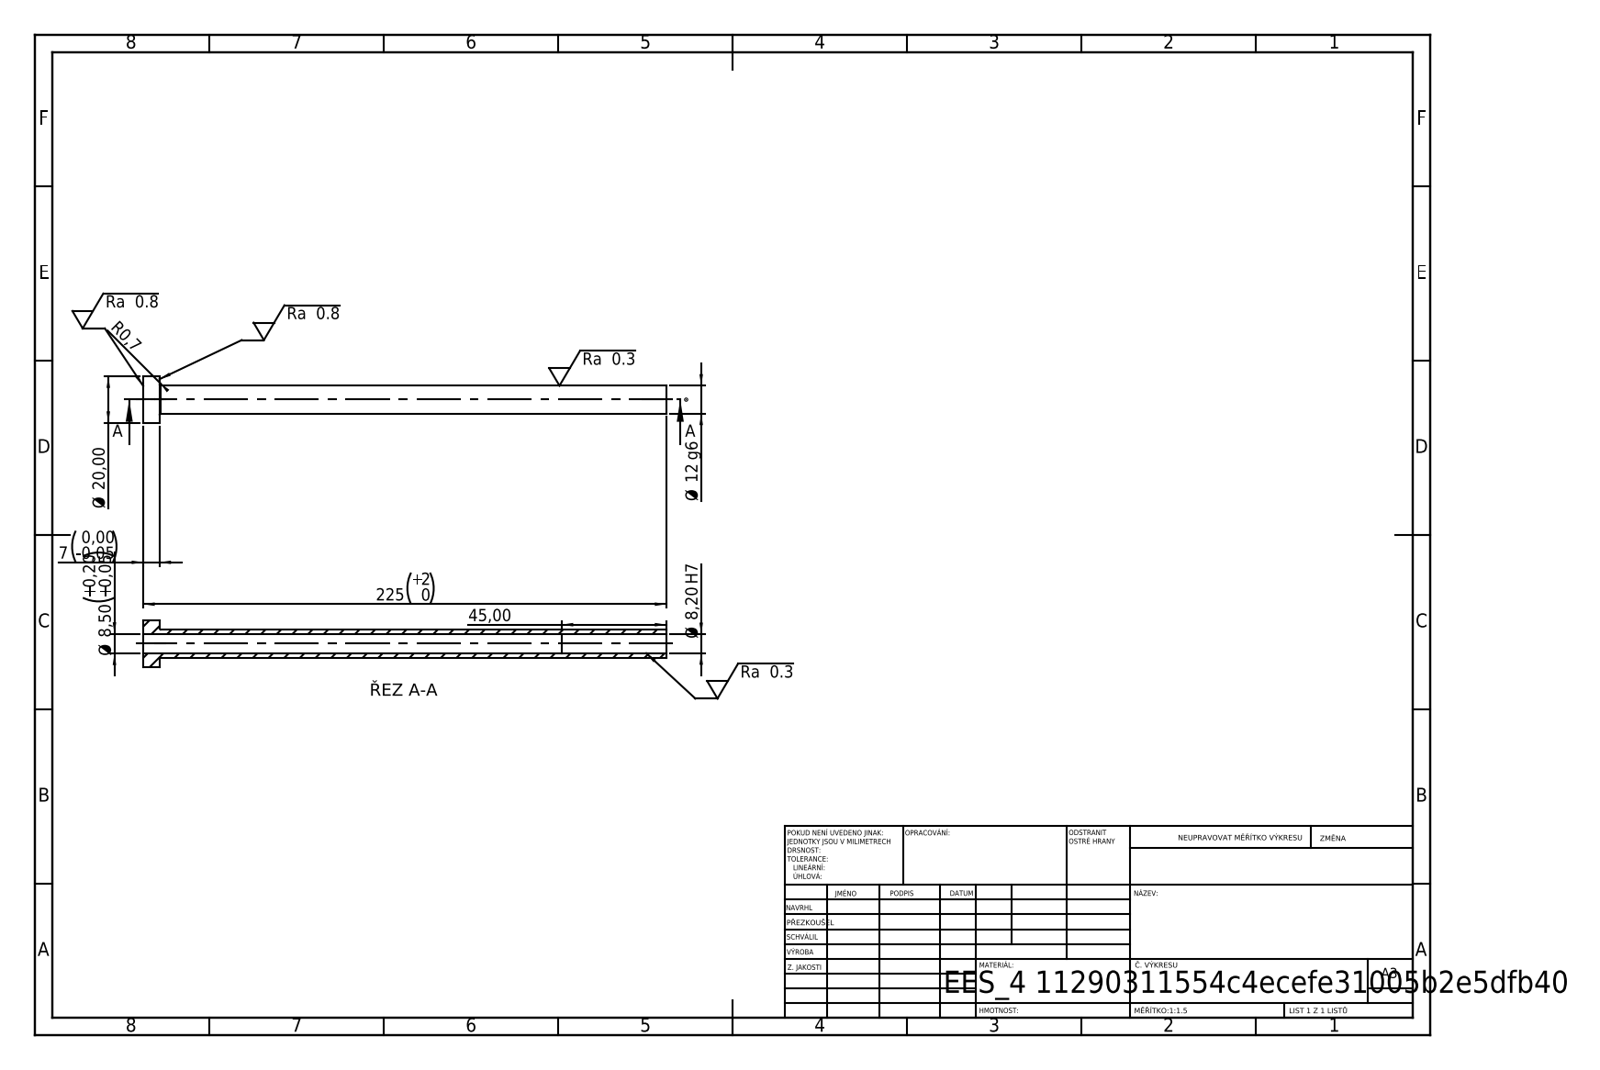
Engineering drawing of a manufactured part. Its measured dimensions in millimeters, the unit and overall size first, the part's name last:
Units: millimetres
Overall size (bounding box): 225 × 20 × 20
Round holes (diameter × count): ⌀8.2 ×1, ⌀8.5 ×1
Round bosses / shafts (diameter × count): ⌀20 ×1, ⌀12 ×1
Main face-to-face distances: 7, 225, 218, 180, 173, 45
Volume: 14 268 mm³ · Surface area: 15 136 mm²
Bodies: 1 solid, 14 faces (4 planar, 8 cylindrical, 2 other)
STEP written by: SolidWorks 2019 (CONFIG_CONTROL_DESIGN)
